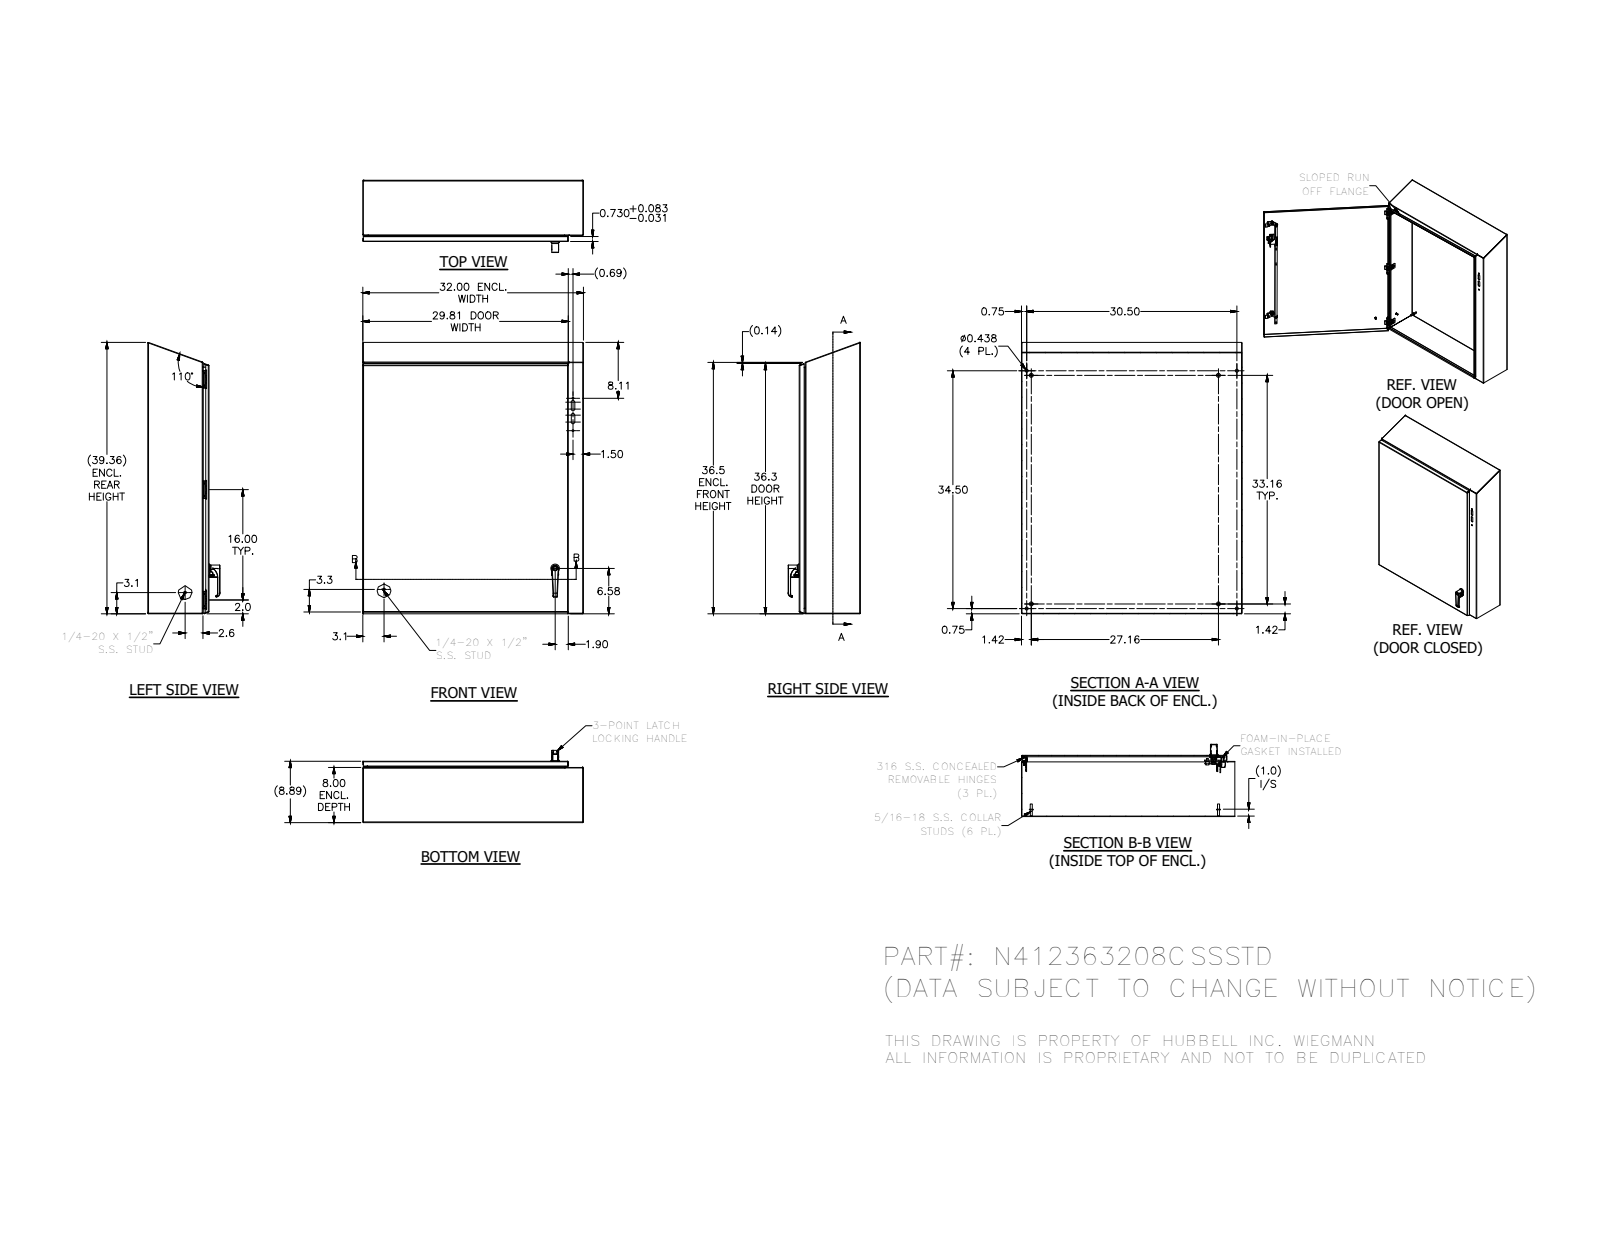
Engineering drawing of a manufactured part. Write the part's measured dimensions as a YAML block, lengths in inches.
part_name: "N412363208CSSSTDB3S; 388151; N4123208CSSSTDTOP; 38846 (+8 more)"
step_written_by: "Autodesk Inventor 2016 (AUTOMOTIVE_DESIGN)"
units: inches
bodies: {solids: 71, faces: 2548, planar: 976, cylindrical: 917, other: 655}
overall_size: [39.357, 32, 10.481]
volume: 290
surface_area: 7790
round_holes:
  - {diameter: 0.093, count: 6}
  - {diameter: 0.145, count: 6}
  - {diameter: 0.152, count: 6}
  - {diameter: 0.156, count: 6}
  - {diameter: 0.167, count: 6}
  - {diameter: 0.172, count: 6}
  - {diameter: 0.187, count: 4}
  - {diameter: 0.437, count: 4}
  - {diameter: 0.32, count: 3}
  - {diameter: 0.196, count: 2}
  - {diameter: 0.211, count: 2}
  - {diameter: 0.22, count: 2}
round_bosses_or_shafts:
  - {diameter: 0.25, count: 16}
  - {diameter: 0.3, count: 8}
  - {diameter: 0.36, count: 6}
  - {diameter: 0.32, count: 6}
  - {diameter: 0.256, count: 6}
  - {diameter: 0.164, count: 6}
  - {diameter: 0.131, count: 6}
  - {diameter: 0.563, count: 4}
partial_cylinders:
  - {radius: 0.02, count: 38}
  - {radius: 0.05, count: 38}
  - {radius: 0.031, count: 33}
  - {radius: 0.125, count: 33}
  - {radius: 0.012, count: 30}
  - {radius: 0.016, count: 26}
  - {radius: 0.105, count: 19}
  - {radius: 0.025, count: 16}
face_to_face_distances: [0.074, 8.813, 8.739, 8.887, 31.926, 7.926, 0.887, 31.852, 32, 0.813]
hole_center_spacings: [16, 0.5, 32, 16.008, 0.656, 0.66, 1.307, 1.311]
